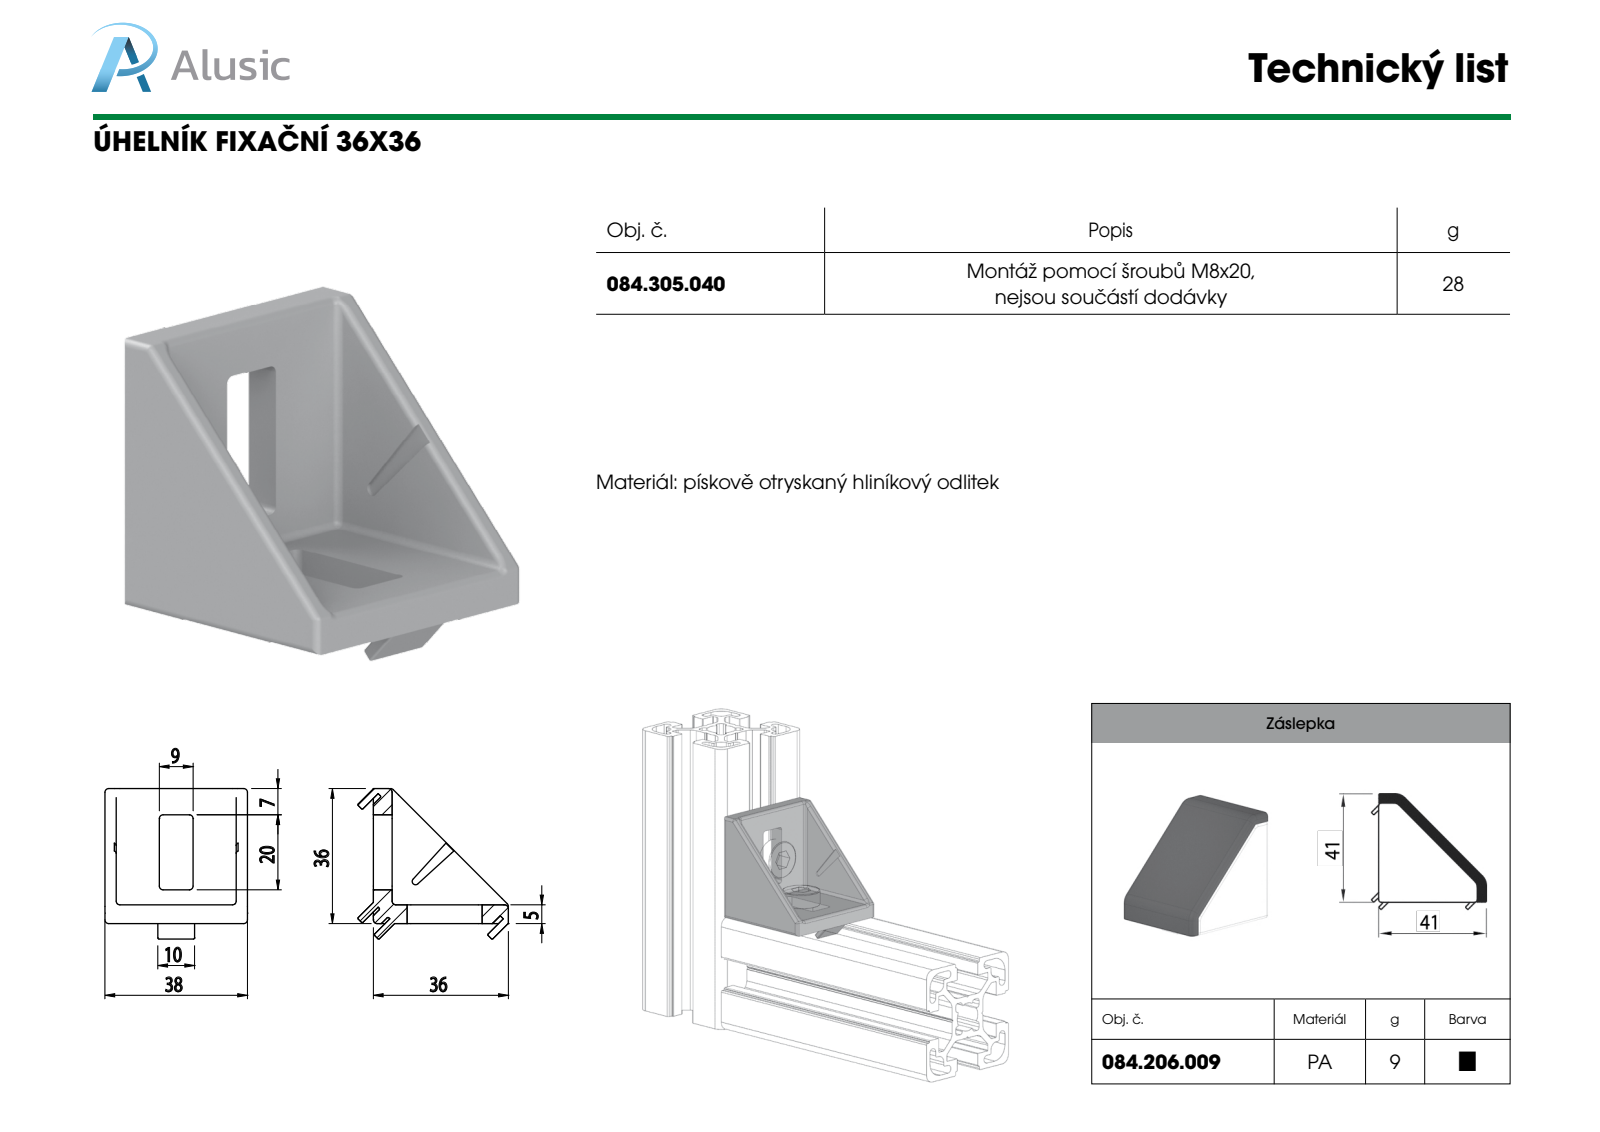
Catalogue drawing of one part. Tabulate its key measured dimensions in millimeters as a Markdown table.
| quantity | value |
| --- | --- |
| part name | 1.ANG.018 |
| STEP written by | SolidWorks 2016 (CONFIG_CONTROL_DESIGN) |
| units | millimeters |
| bodies | 1 solid, 77 faces (69 planar, 8 cylindrical, 0 other) |
| overall size | 38.83 × 38.83 × 38 |
| volume | 15 724 mm³ |
| surface area | 9 383 mm² |
| partial cylindrical surfaces (radius × count) | 2 × 8 |
| main face-to-face distances | 4.5, 38, 4, 12, 34, 8, 3.5, 9, 36, 32.5 |
